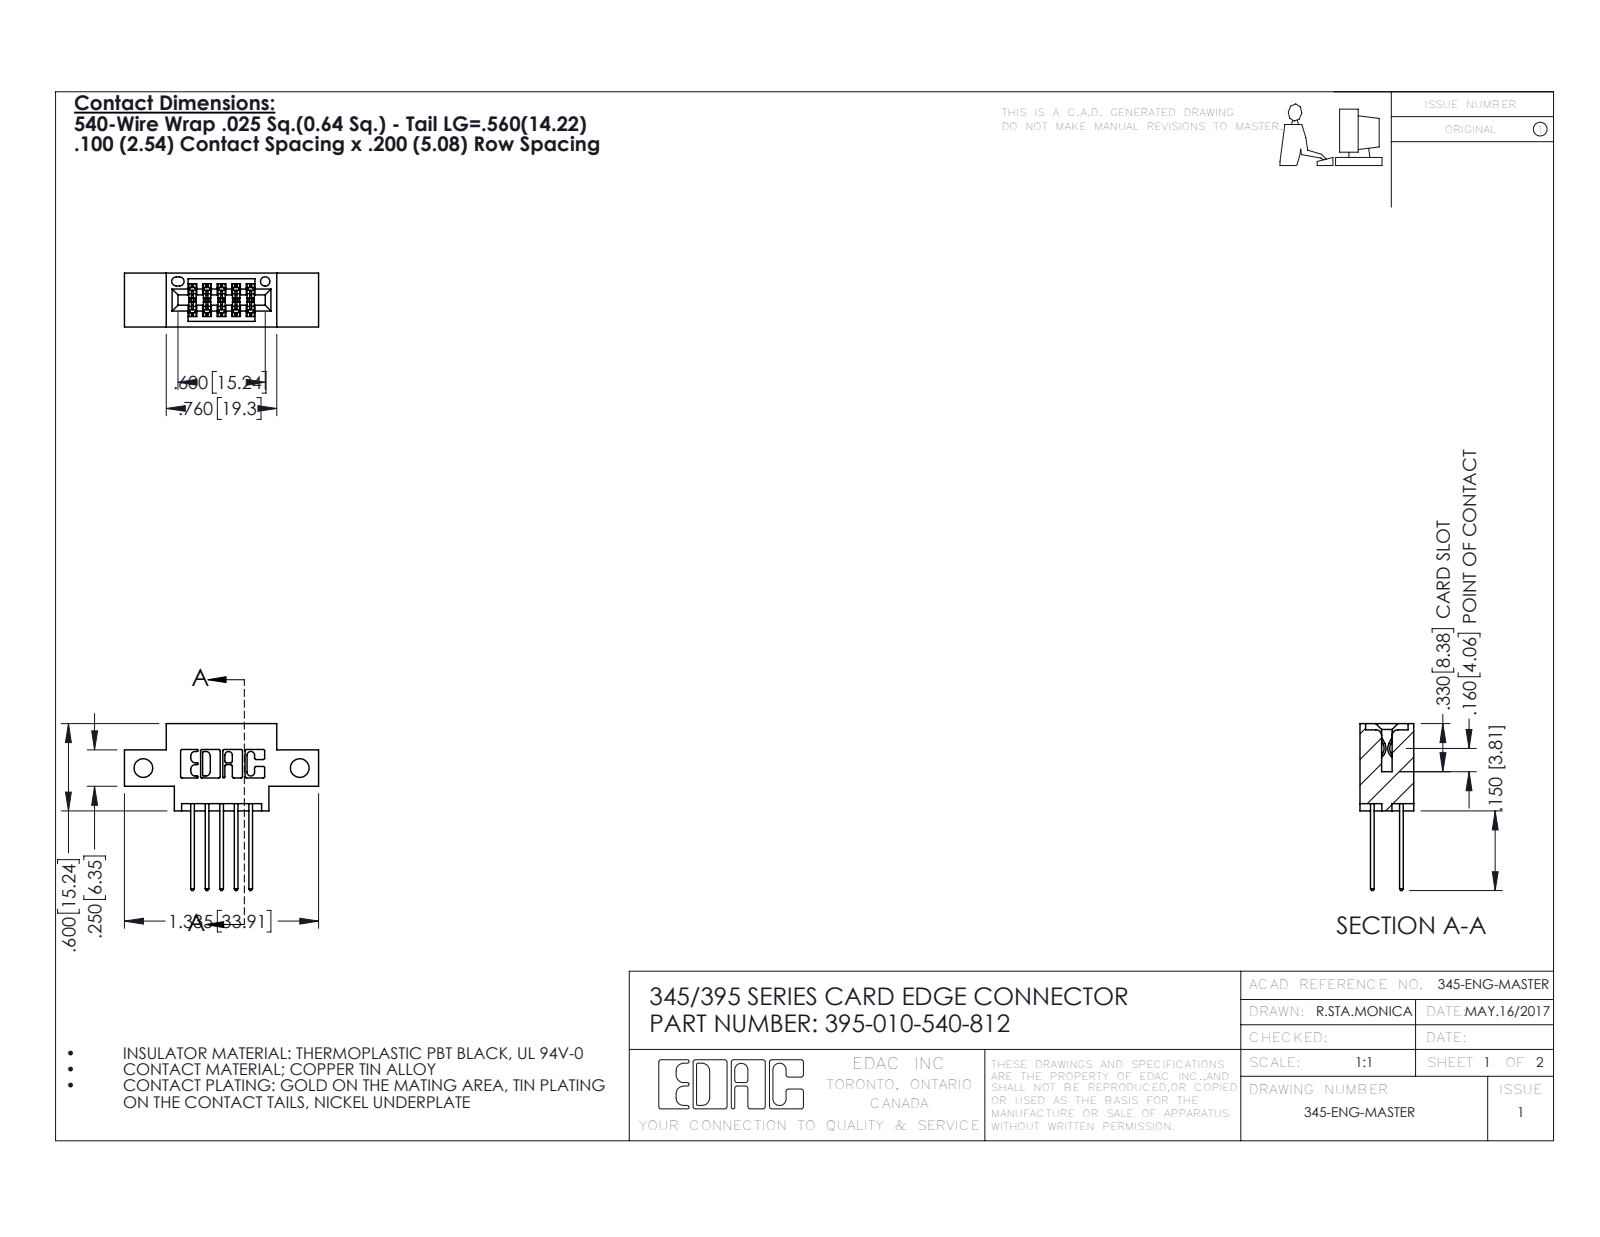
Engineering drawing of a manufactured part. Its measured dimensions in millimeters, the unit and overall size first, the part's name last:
Units: millimetres
Overall size (bounding box): 33.9 × 29.1 × 9.4
Round holes (diameter × count): ⌀3.3 ×2, ⌀1.6 ×1
Partial cylindrical surfaces — rounded edges, fillets, slot ends (radius × count): R0.3 ×22, R0.2 ×15, R0.3 ×10, R0.2 ×6, R0.8 ×6, R0.7 ×3, R0.4 ×2, R0.5 ×2
Main face-to-face distances: 5.1, 9.4, 7.6, 1.8, 2.5, 2.5, 6.9, 0.6, 6.4, 5.7
Hole centre spacings: 27.3
Volume: 2 790 mm³ · Surface area: 3 588 mm²
Bodies: 11 solids, 630 faces (414 planar, 216 cylindrical, 0 other)
Part name (STEP PRODUCT): 345 Part_0.170 Offset - Side Mount; 395-010-540-812; 345-292-001_345-293-140
STEP written by: SolidWorks 2016 (CONFIG_CONTROL_DESIGN)
